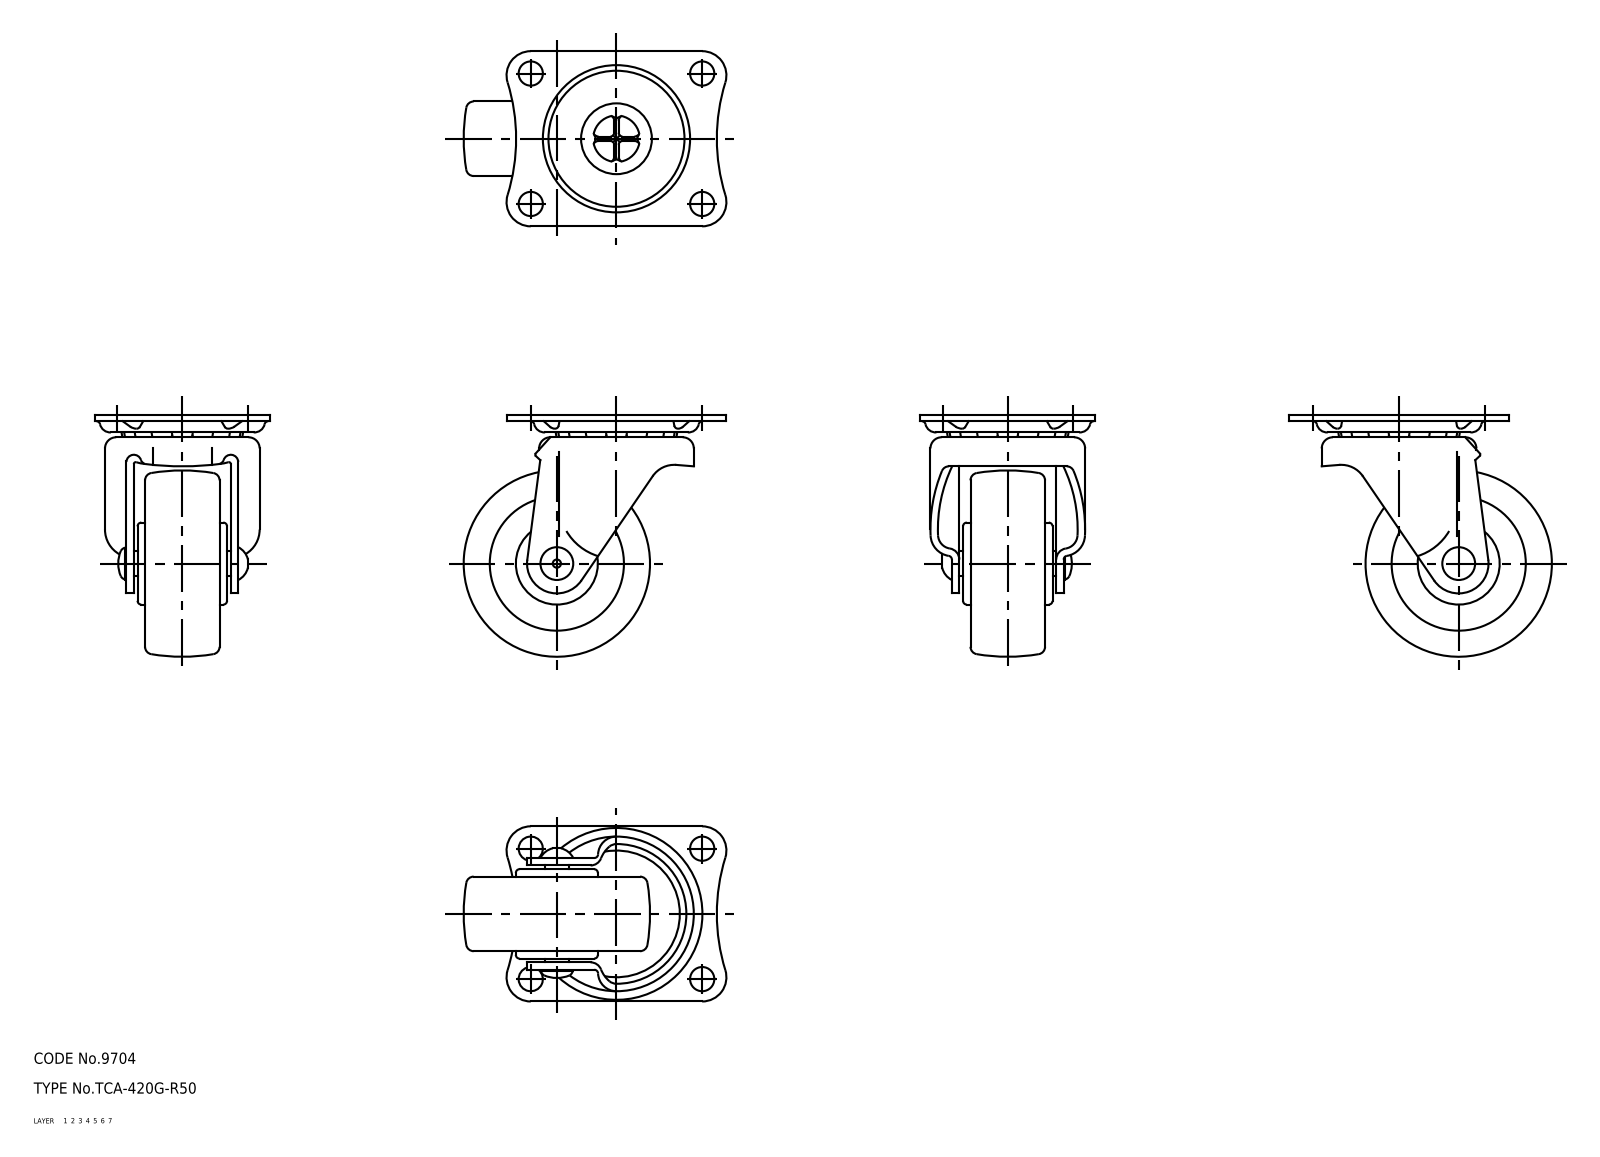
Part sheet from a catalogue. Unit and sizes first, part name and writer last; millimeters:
Units: millimetres
Overall size (bounding box): 70.5 × 65 × 47
Volume: 51 771 mm³ · Surface area: 24 144 mm²
Bodies: 5 solids, 286 faces (0 planar, 0 cylindrical, 286 other)
Part name (STEP PRODUCT): wheel; mounting plate; main shaft; axle (+1 more)
STEP written by: CADfix (AUTOMOTIVE_DESIGN)
